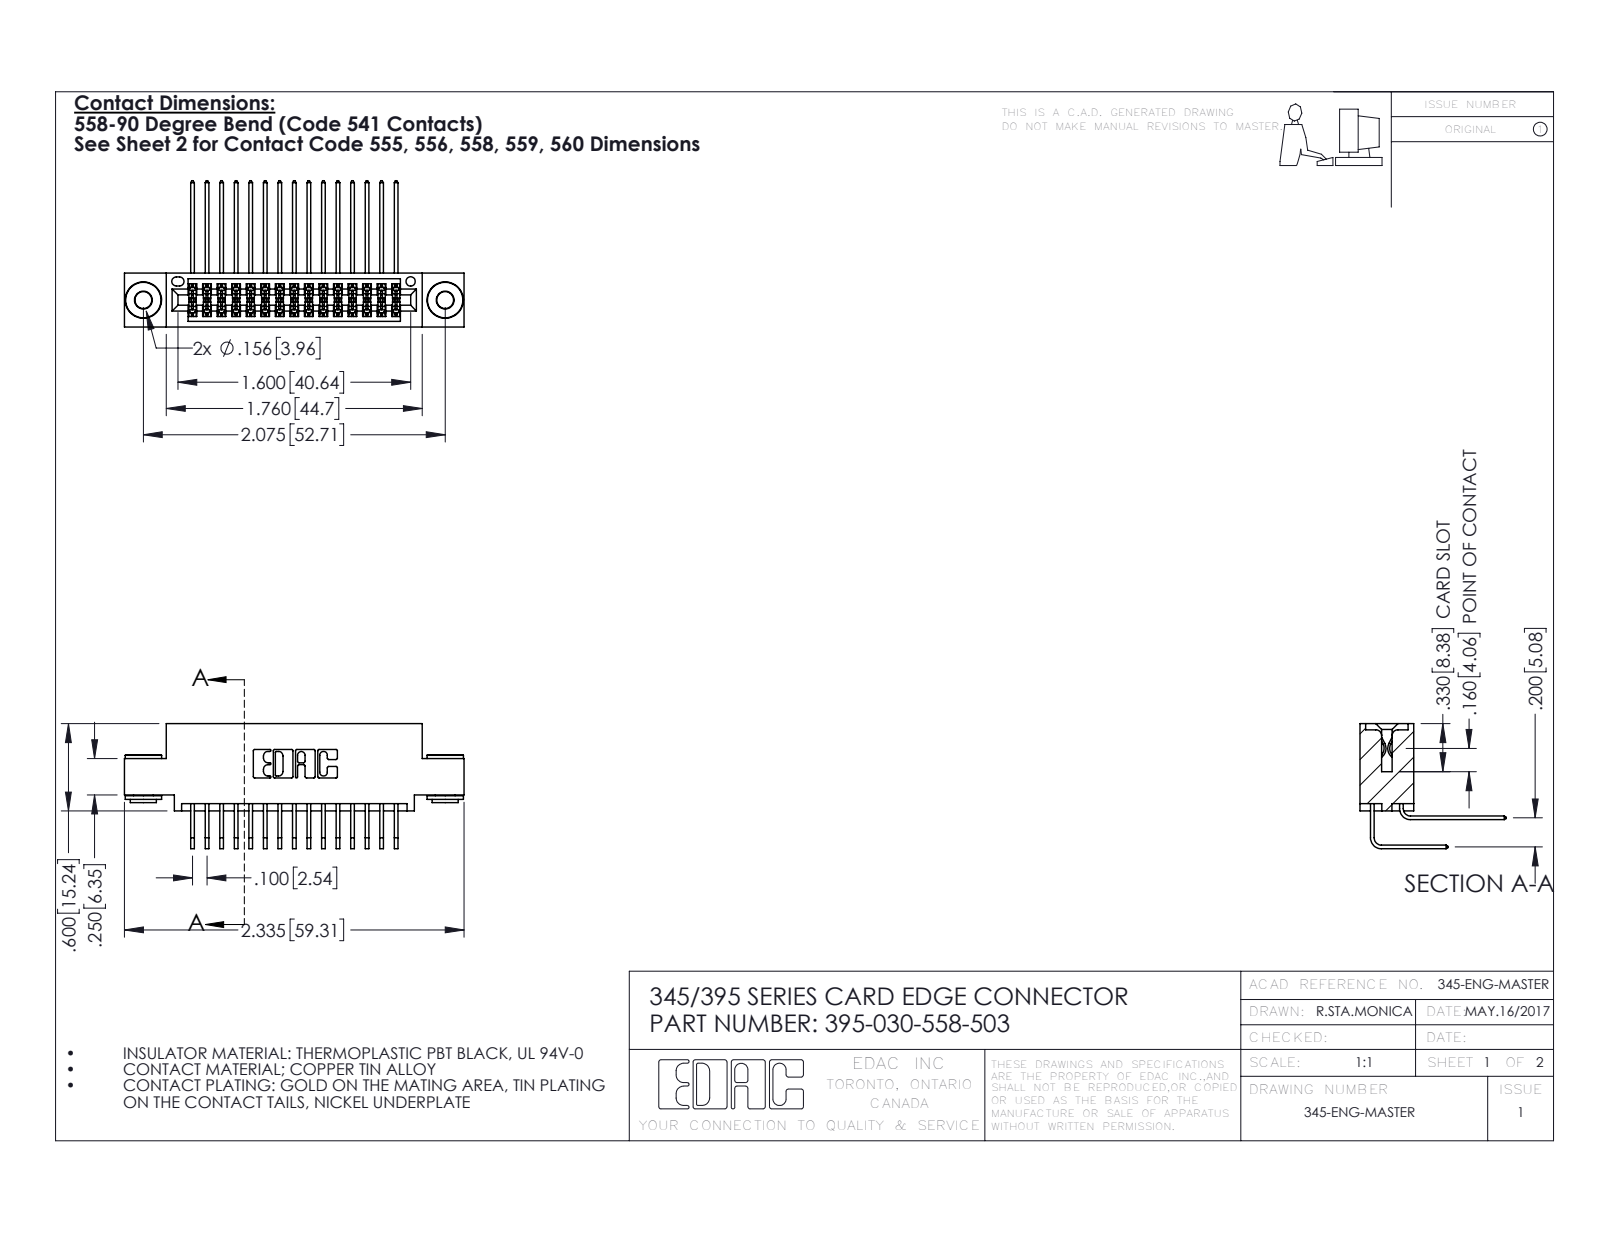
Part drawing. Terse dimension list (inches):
name: 345-250-002_345-250-002-102; 345 Part_0.110 Offset - 0.156 Dia-TH; 345-292-001_558 559 Tail - 1; 395-030-558-503 (+1 more)
written by: SolidWorks 2016 (CONFIG_CONTROL_DESIGN)
unit: in
bodies: 33 solids, 1728 faces (1144 planar, 576 cylindrical, 8 other)
size: 2.335 × 1.005 × 0.859
volume: 0.344 in³; area: 13.81 in²
holes: 2× ⌀0.116, 2× ⌀0.156, 1× ⌀0.064
bosses: 2× ⌀0.25, 2× ⌀0.18, 2× ⌀0.136
rounds: 46× R0.006, 22× R0.01, 6× R0.007, 6× R0.031, 3× R0.026, 2× R0.014, 2× R0.019, 2× R0.022
face distances: 0.2, 0.072, 0.298, 0.37, 0.025, 0.098, 0.272, 0.225, 0.1, 0.025
hole spacings: 0.27, 1.842, 2.075
